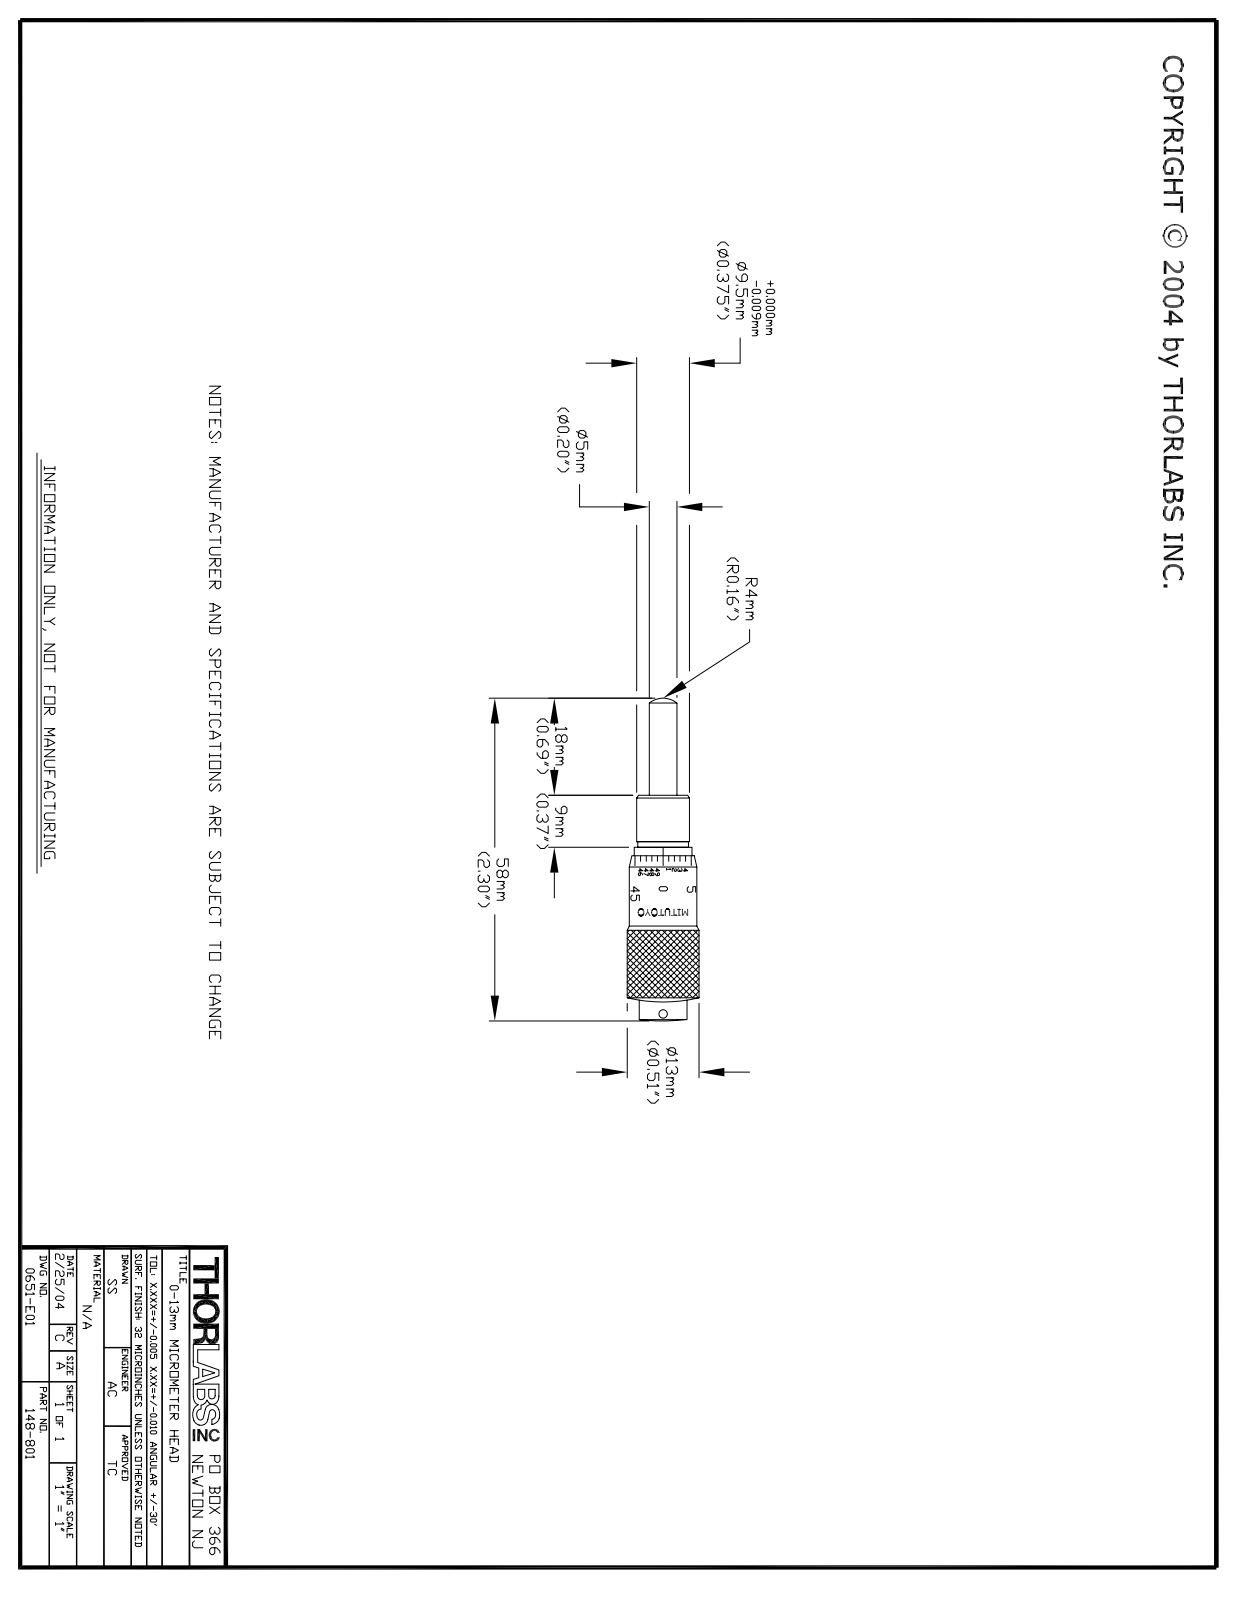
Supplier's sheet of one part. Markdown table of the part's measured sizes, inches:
| quantity | value |
| --- | --- |
| part name | 0651-E0W |
| STEP written by | SolidWorks 2007 (AUTOMOTIVE_DESIGN) |
| units | inches |
| bodies | 0 solids, 32 faces (4 planar, 16 cylindrical, 12 other) |
| overall size | 2.295 × 0.51 × 0.51 |
| round holes (diameter × count) | 0.06 × 1 |
| round bosses / shafts (diameter × count) | 0.51 × 1, 0.48 × 1, 0.41 × 1, 0.375 × 1, 0.36 × 1, 0.34 × 1, 0.197 × 1 |
| main face-to-face distances | 0.37, 0.43, 0.06, 0.33, 0.04, 0.1 |
